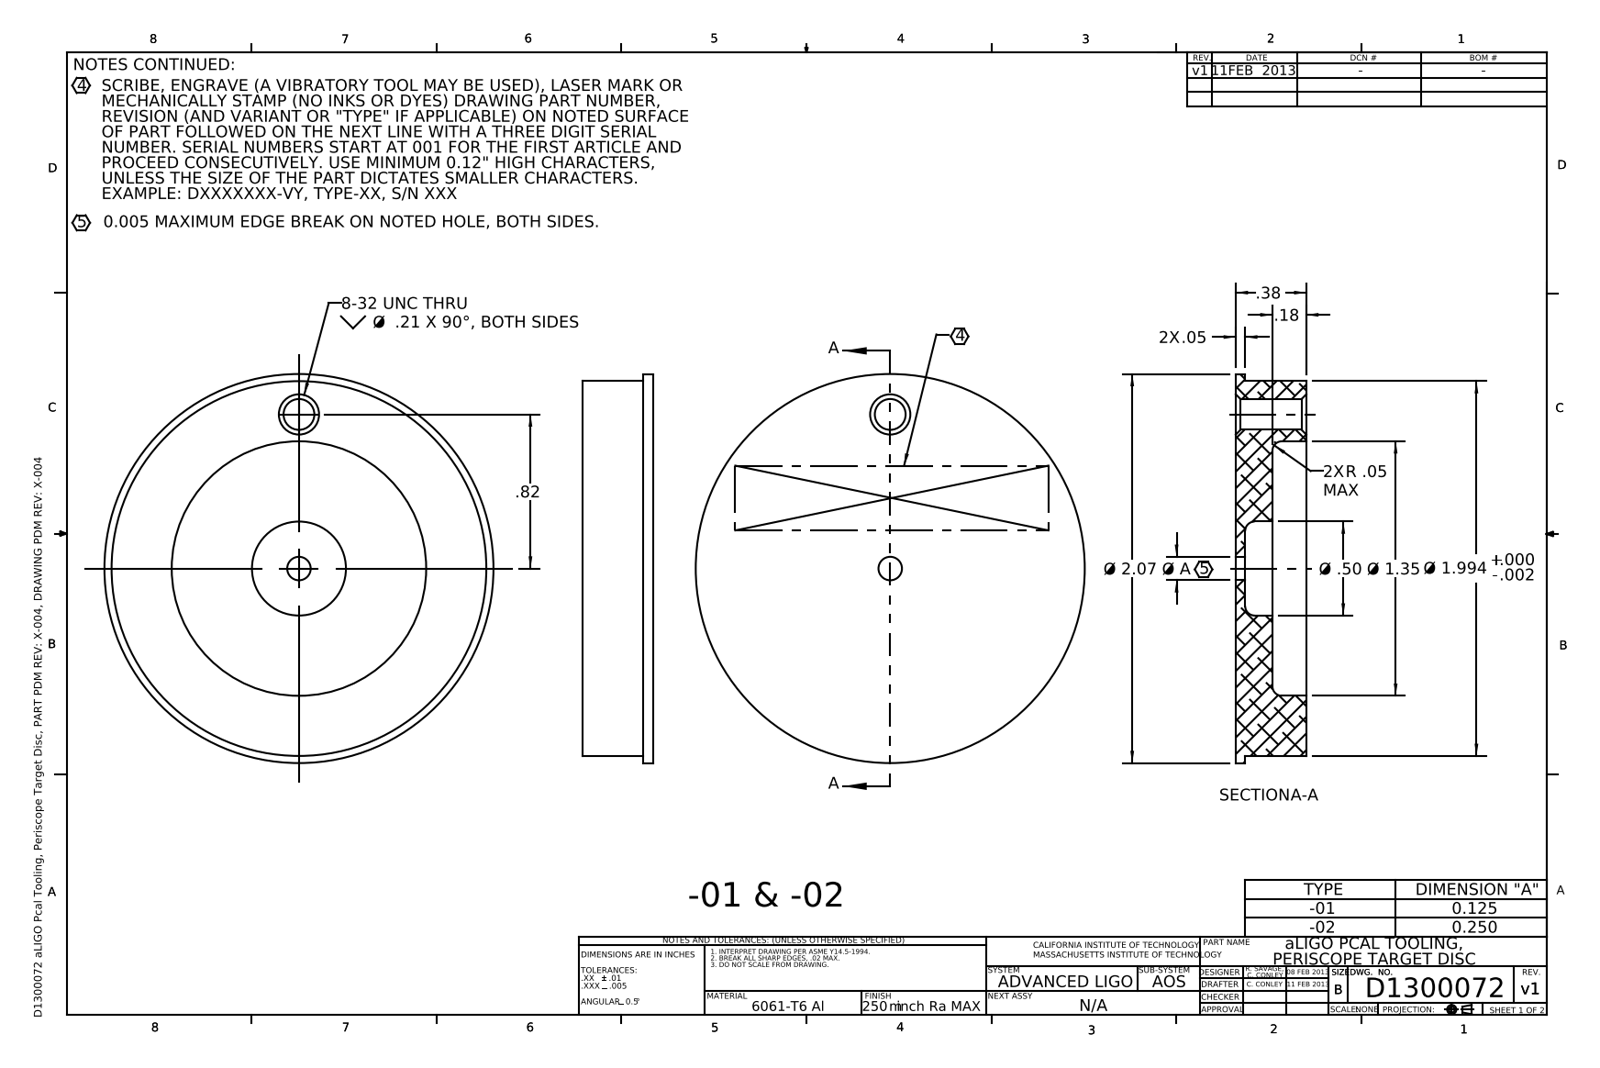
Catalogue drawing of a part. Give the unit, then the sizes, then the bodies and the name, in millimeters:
Units: millimetres
Overall size (bounding box): 52.6 × 52.6 × 9.5
Round holes (diameter × count): ⌀3.2 ×1, ⌀4.2 ×1, ⌀12.7 ×1, ⌀34.4 ×1
Round bosses / shafts (diameter × count): ⌀52.6 ×1, ⌀50.6 ×1
Main face-to-face distances: 9.5, 4.6, 5, 8.3, 3.7, 1.3
Hole centre spacings: 20.8
Volume: 14 600 mm³ · Surface area: 6 510 mm²
Bodies: 1 solid, 25 faces (5 planar, 12 cylindrical, 8 other)
Part name (STEP PRODUCT): D1300072-v1 aLIGO Pcal Tooling, Periscope Target Disc
STEP written by: SolidWorks 2012 (AUTOMOTIVE_DESIGN)
